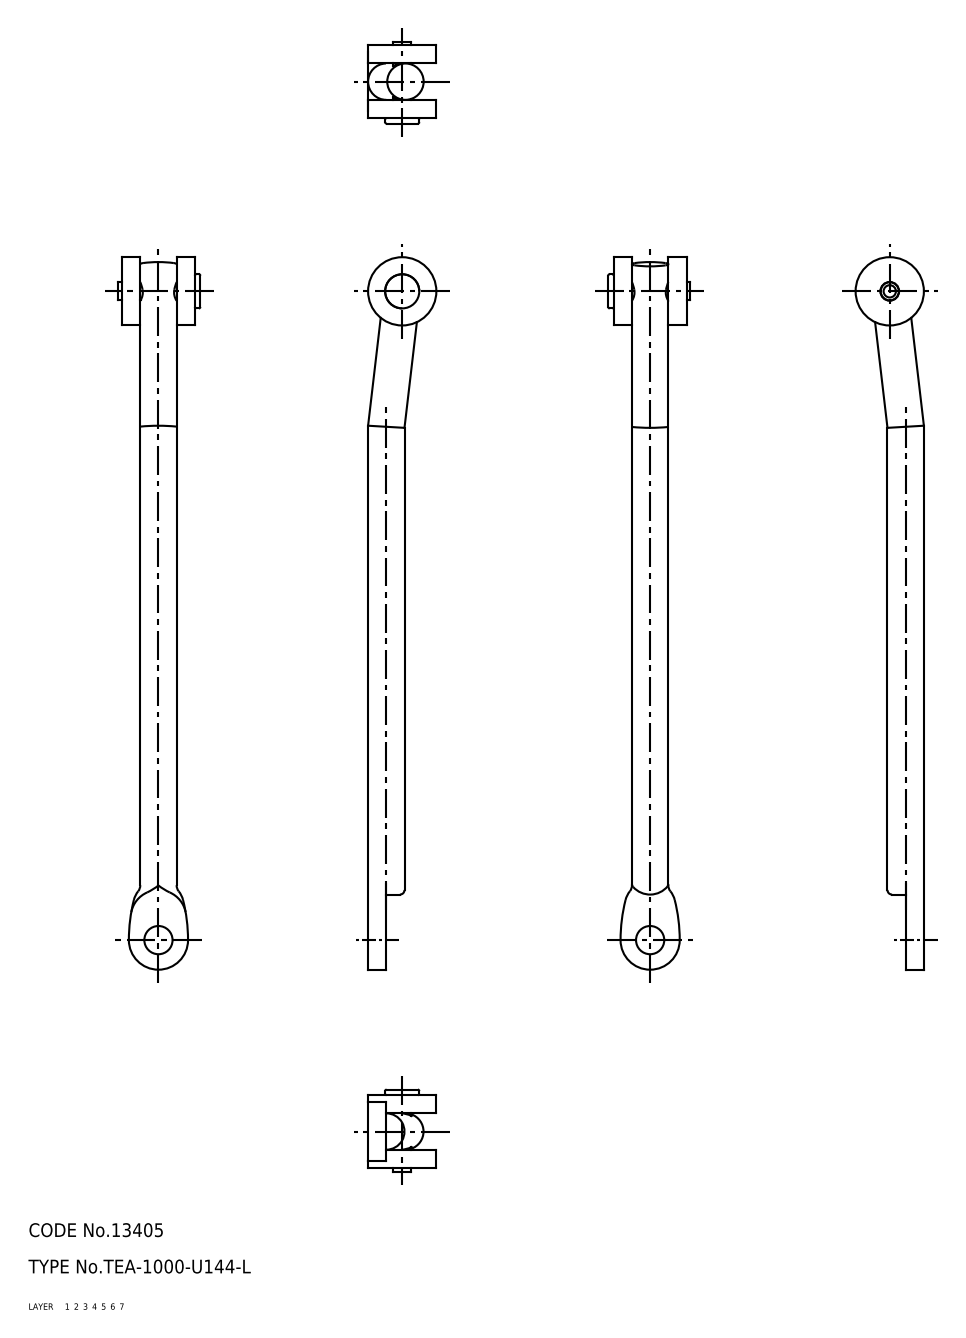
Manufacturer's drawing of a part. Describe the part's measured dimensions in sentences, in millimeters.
The part is named "roller; rod; TEA_1000_U144_L_7253_36". Its 3-D file was written by "CADfix (AUTOMOTIVE_DESIGN)". It is 2 solids with 49 faces: 0 planar, 0 cylindrical and 49 other. Overall it measures 156.57 by 18 by 15 millimeters. Its volume is 9 043 cubic millimeters and its surface area 5 402 square millimeters.
